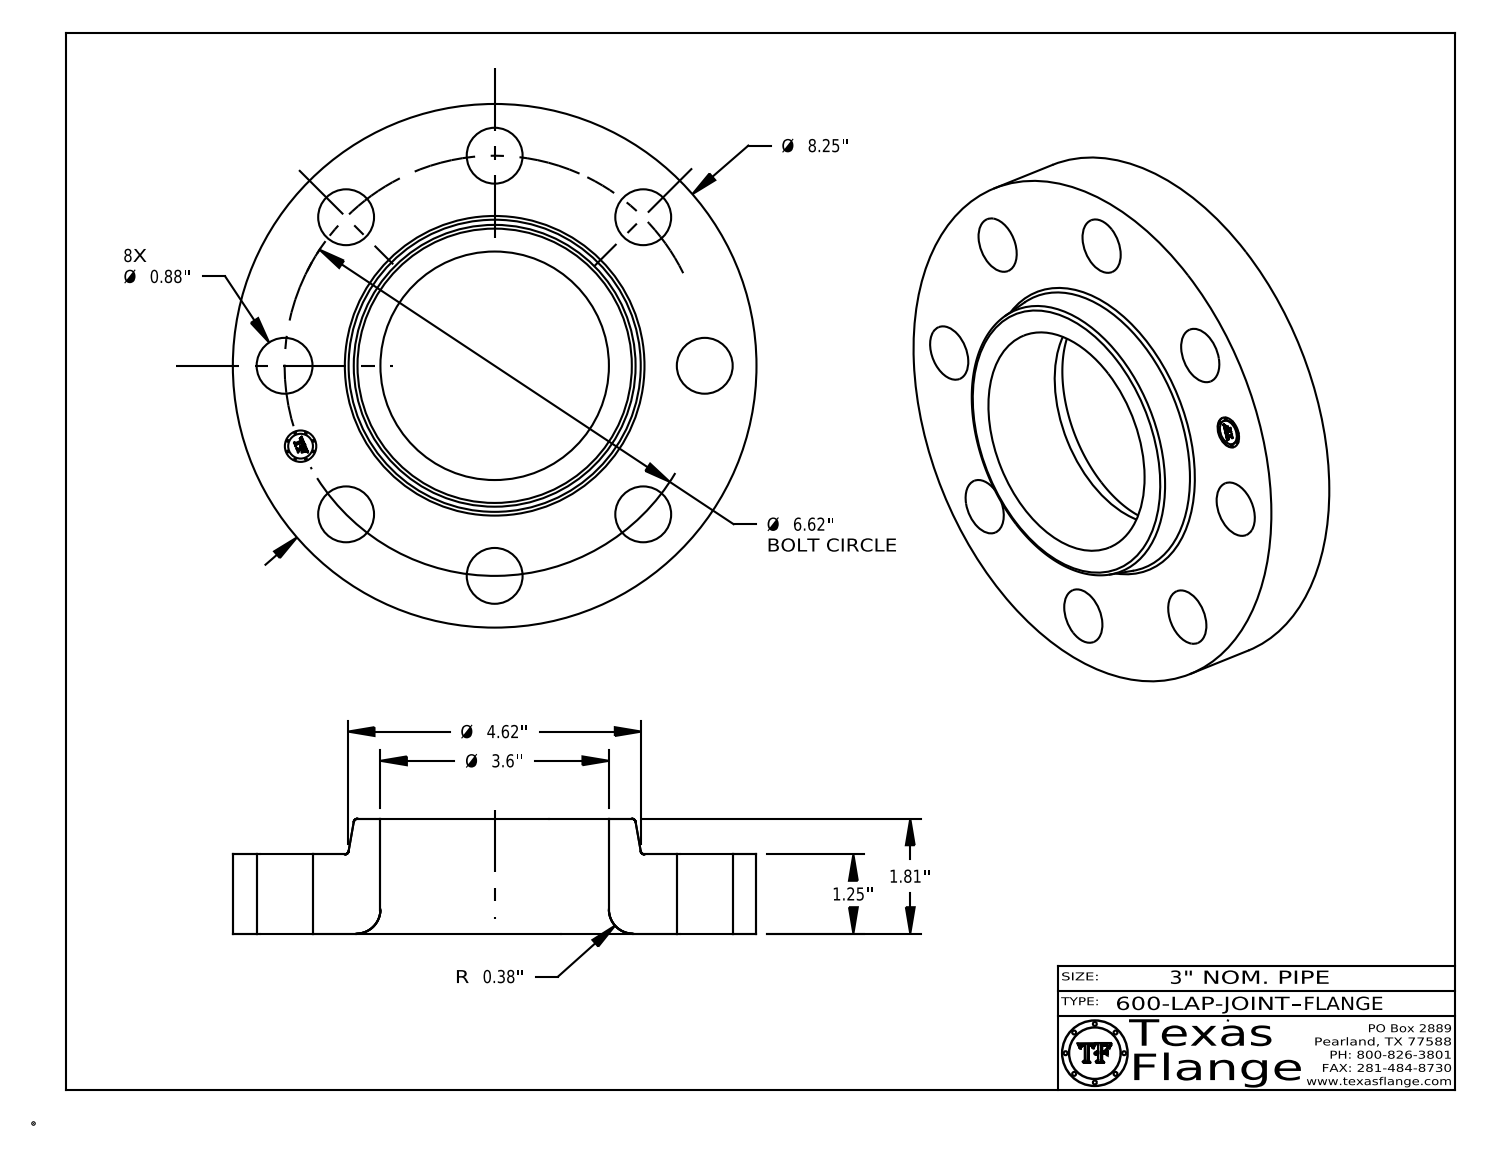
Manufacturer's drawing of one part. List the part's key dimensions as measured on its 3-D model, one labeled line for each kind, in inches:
Part name (STEP PRODUCT): 600-LAP-JOINT FLANGE
STEP written by: CATIA V5 STEP AP214 (AUTOMOTIVE_DESIGN)
Units: inches
Bodies: 1 solid, 416 faces (368 planar, 40 cylindrical, 8 other)
Overall size (bounding box): 8.25 × 8.25 × 1.81
Volume: 50.94 in³ · Surface area: 161.8 in²
Round holes (diameter × count): ⌀0.88 ×8, ⌀0.495 ×1, ⌀3.6 ×1
Round bosses / shafts (diameter × count): ⌀0.03 ×8, ⌀8.25 ×1, ⌀0.39 ×1
Main face-to-face distances: 1.25, 1.81, 0.56, 0.015, 1.235, 0.575, 0.148, 0.145, 0.027, 0.096
Hole centre spacings: 3.31, 2.533, 6.116, 4.681, 4.681, 1.291, 3.678, 6.493
